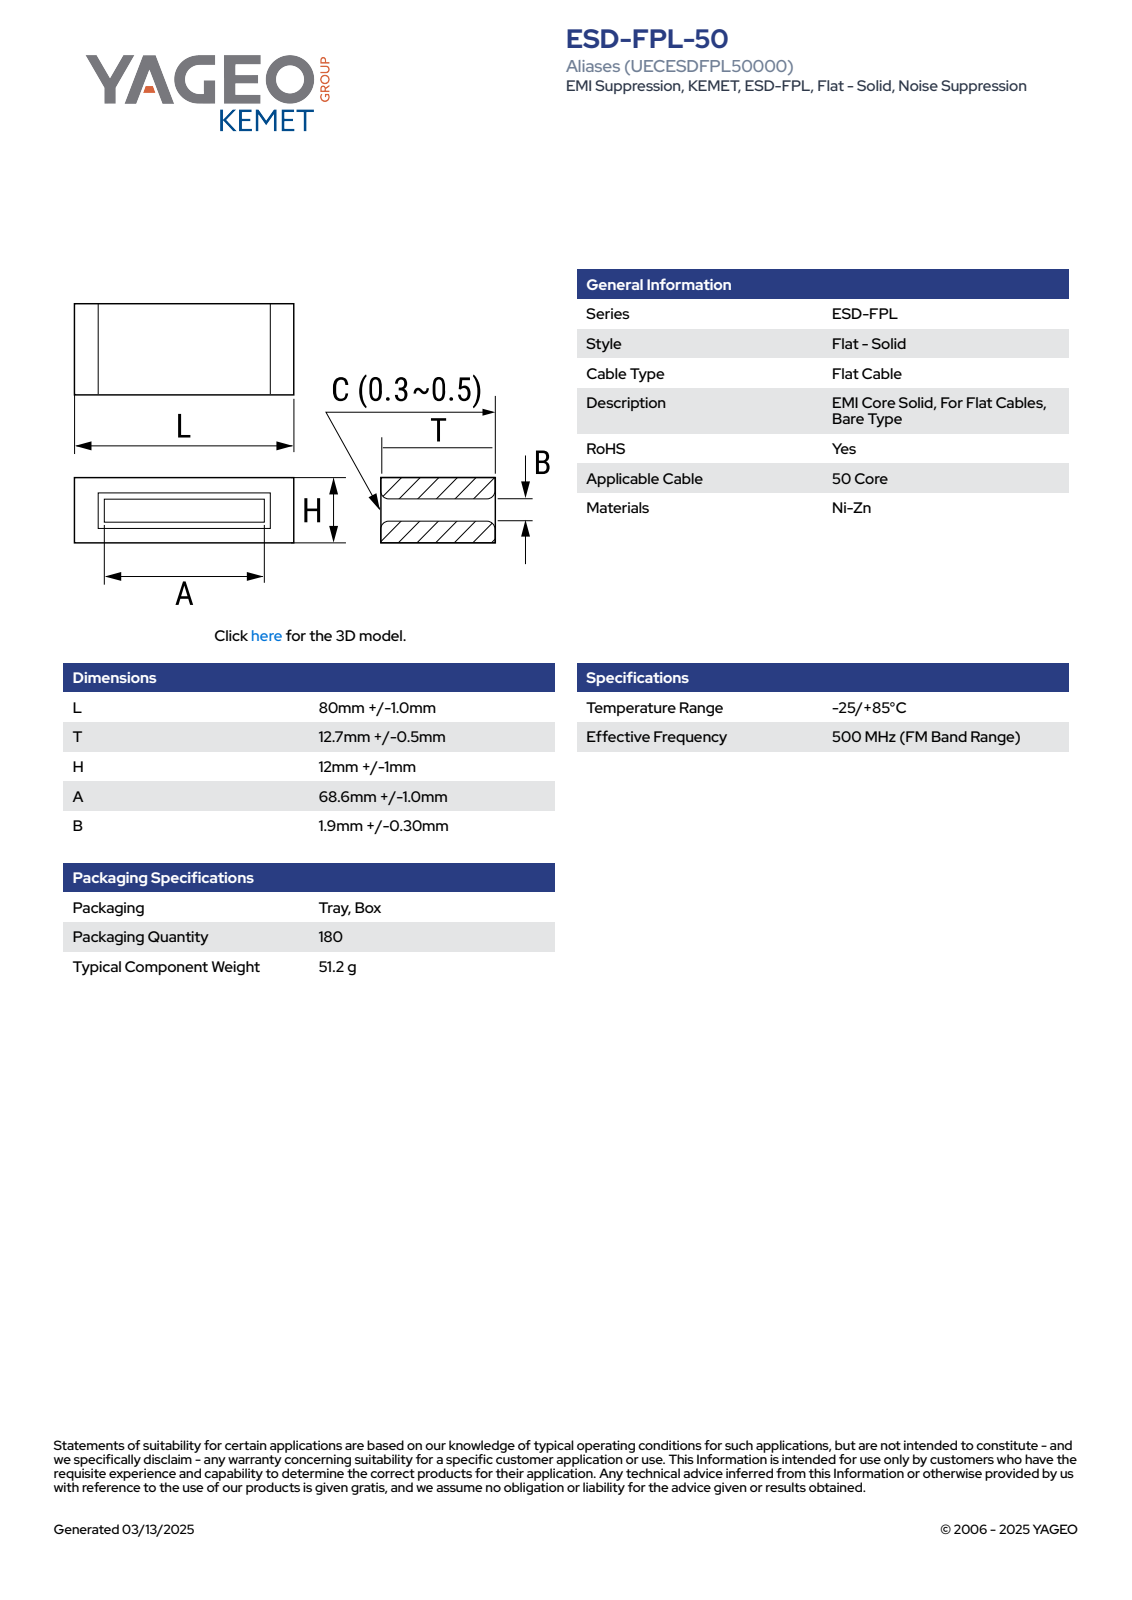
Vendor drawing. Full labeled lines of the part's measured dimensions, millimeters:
Part name (STEP PRODUCT): EC_FPL1_L81T13.2H13A68.6B1.9
STEP written by: SolidWorks 2021 (AUTOMOTIVE_DESIGN)
Units: millimetres
Bodies: 4 solids, 83 faces (75 planar, 8 cylindrical, 0 other)
Overall size (bounding box): 81 × 13 × 12.7
Volume: 11 656 mm³ · Surface area: 5 907 mm²
Partial cylindrical surfaces — rounded edges, fillets, slot ends (radius × count): R0.5 ×8
Main face-to-face distances: 5.55, 7.45, 13, 1.9, 12.7, 81, 17.47, 6.2, 74.8, 68.6
